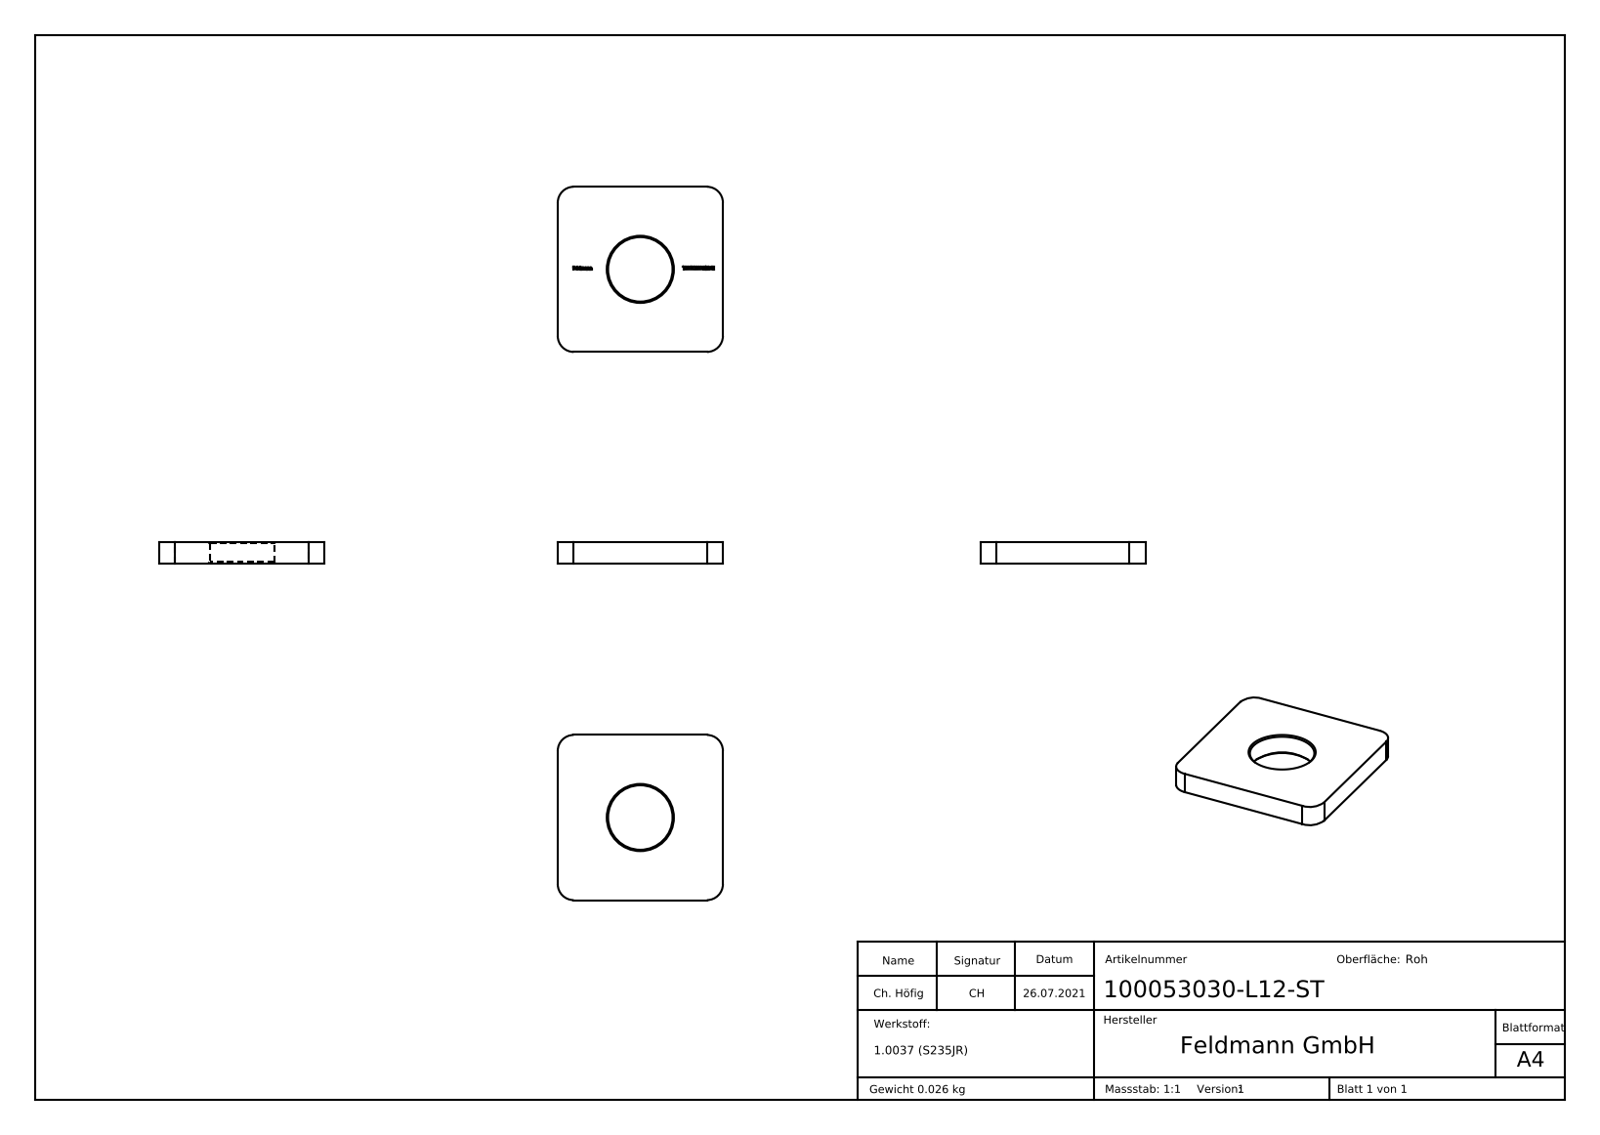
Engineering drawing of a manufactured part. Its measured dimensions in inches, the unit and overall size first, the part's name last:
Units: inches
Overall size (bounding box): 1.22 × 1.22 × 0.157
Round holes (diameter × count): ⌀0.476 ×1
Partial cylindrical surfaces — rounded edges, fillets, slot ends (radius × count): R0.118 ×4
Main face-to-face distances: 0.157, 1.22, 0.154, 0.61, 0.931, 0.147, 0.167, 0.02, 0.784, 0.933
Volume: 0.204 in³ · Surface area: 3.562 in²
Bodies: 1 solid, 303 faces (146 planar, 5 cylindrical, 152 other)
Part name (STEP PRODUCT): 100053030-L12-ST
STEP written by: SolidWorks 2018 (CONFIG_CONTROL_DESIGN)
